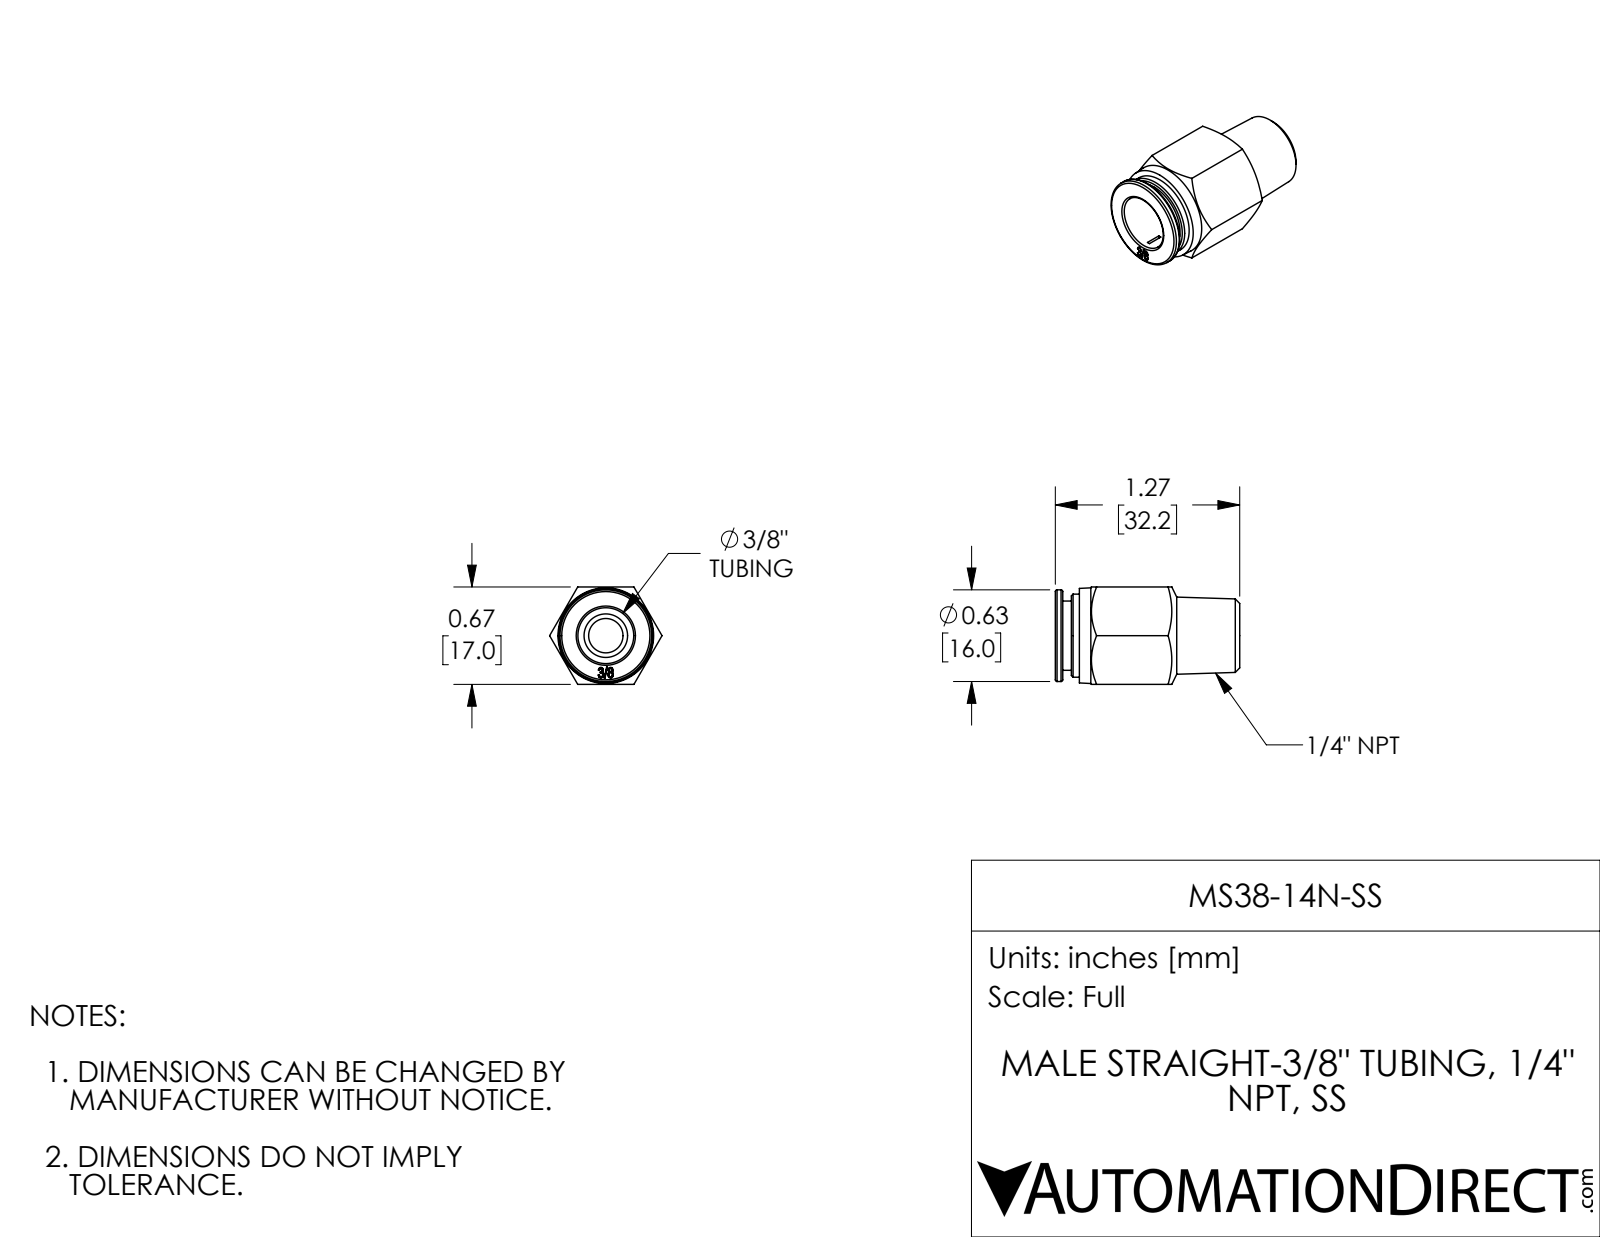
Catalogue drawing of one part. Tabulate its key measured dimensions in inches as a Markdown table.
| quantity | value |
| --- | --- |
| part name | MS38-14N-SS |
| STEP written by | SolidWorks 2017 (AUTOMOTIVE_DESIGN) |
| units | inches |
| bodies | 1 solid, 91 faces (31 planar, 10 cylindrical, 50 other) |
| overall size | 1.268 × 0.773 × 0.669 |
| volume | 0.268 in³ |
| surface area | 4.73 in² |
| round holes (diameter × count) | 0.236 × 1, 0.384 × 1 |
| round bosses / shafts (diameter × count) | 0.63 × 1, 0.571 × 1, 0.476 × 1 |
| main face-to-face distances | 0.669, 0.051, 1.217, 1.268, 1.102, 0.114, 0.165, 0.488, 0.614, 0.728 |
